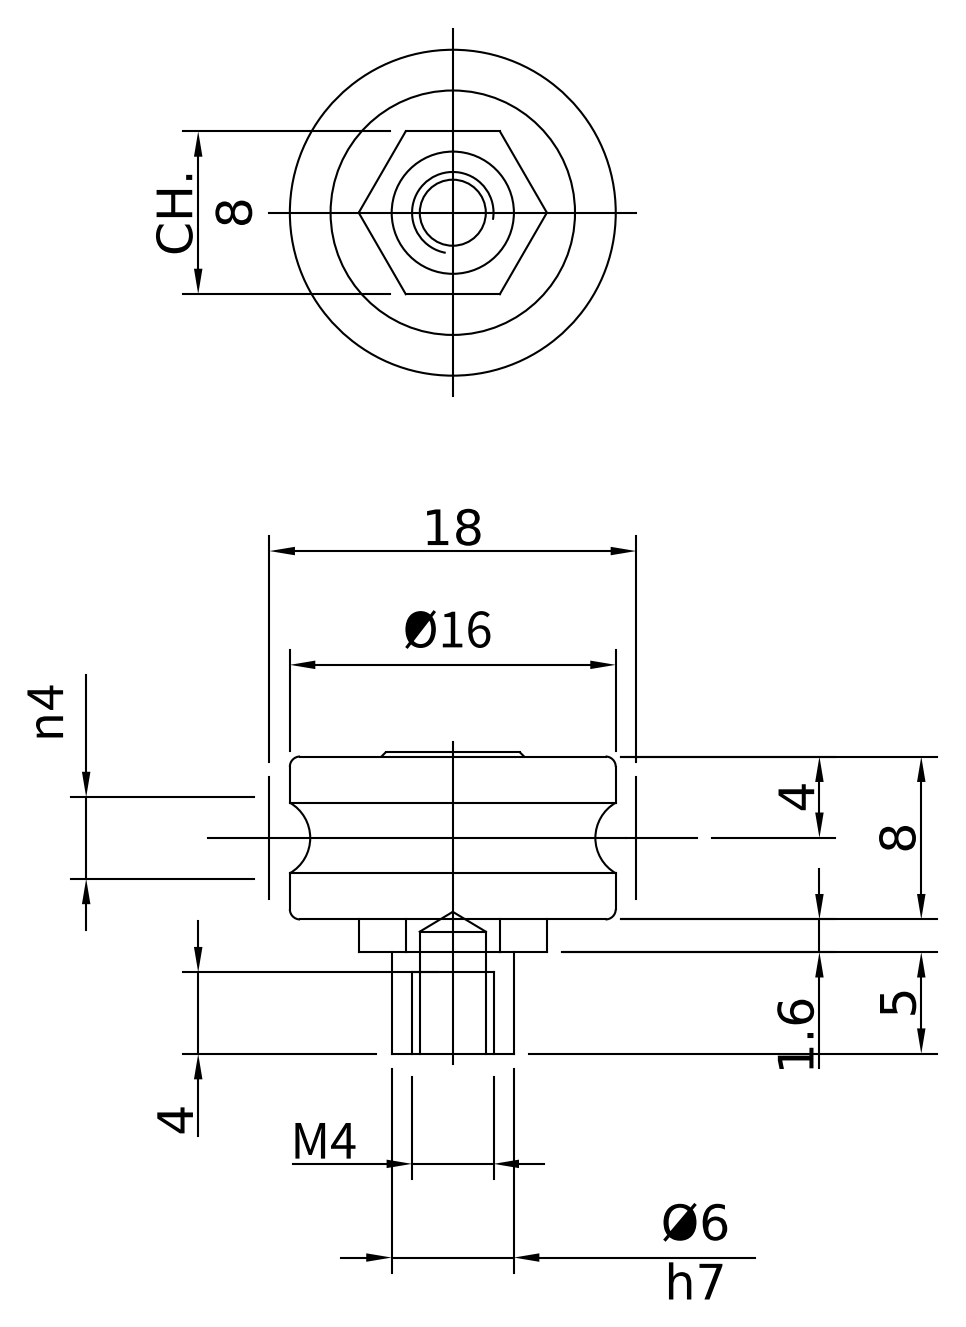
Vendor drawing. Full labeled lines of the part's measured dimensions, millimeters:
Part name (STEP PRODUCT): 23.516.00C
STEP written by: Autodesk Inventor 2022 (AUTOMOTIVE_DESIGN)
Units: millimetres
Bodies: 1 solid, 27 faces (14 planar, 8 cylindrical, 5 other)
Overall size (bounding box): 16 × 16 × 14.8
Volume: 1 626 mm³ · Surface area: 1 074 mm²
Round holes (diameter × count): ⌀3.24 ×1, ⌀12 ×1
Round bosses / shafts (diameter × count): ⌀16 ×1, ⌀7 ×1, ⌀6 ×1
Main face-to-face distances: 7.7, 8, 7.4, 8.2, 7.9, 0.5, 1.6, 1.9, 9.3, 9.6
